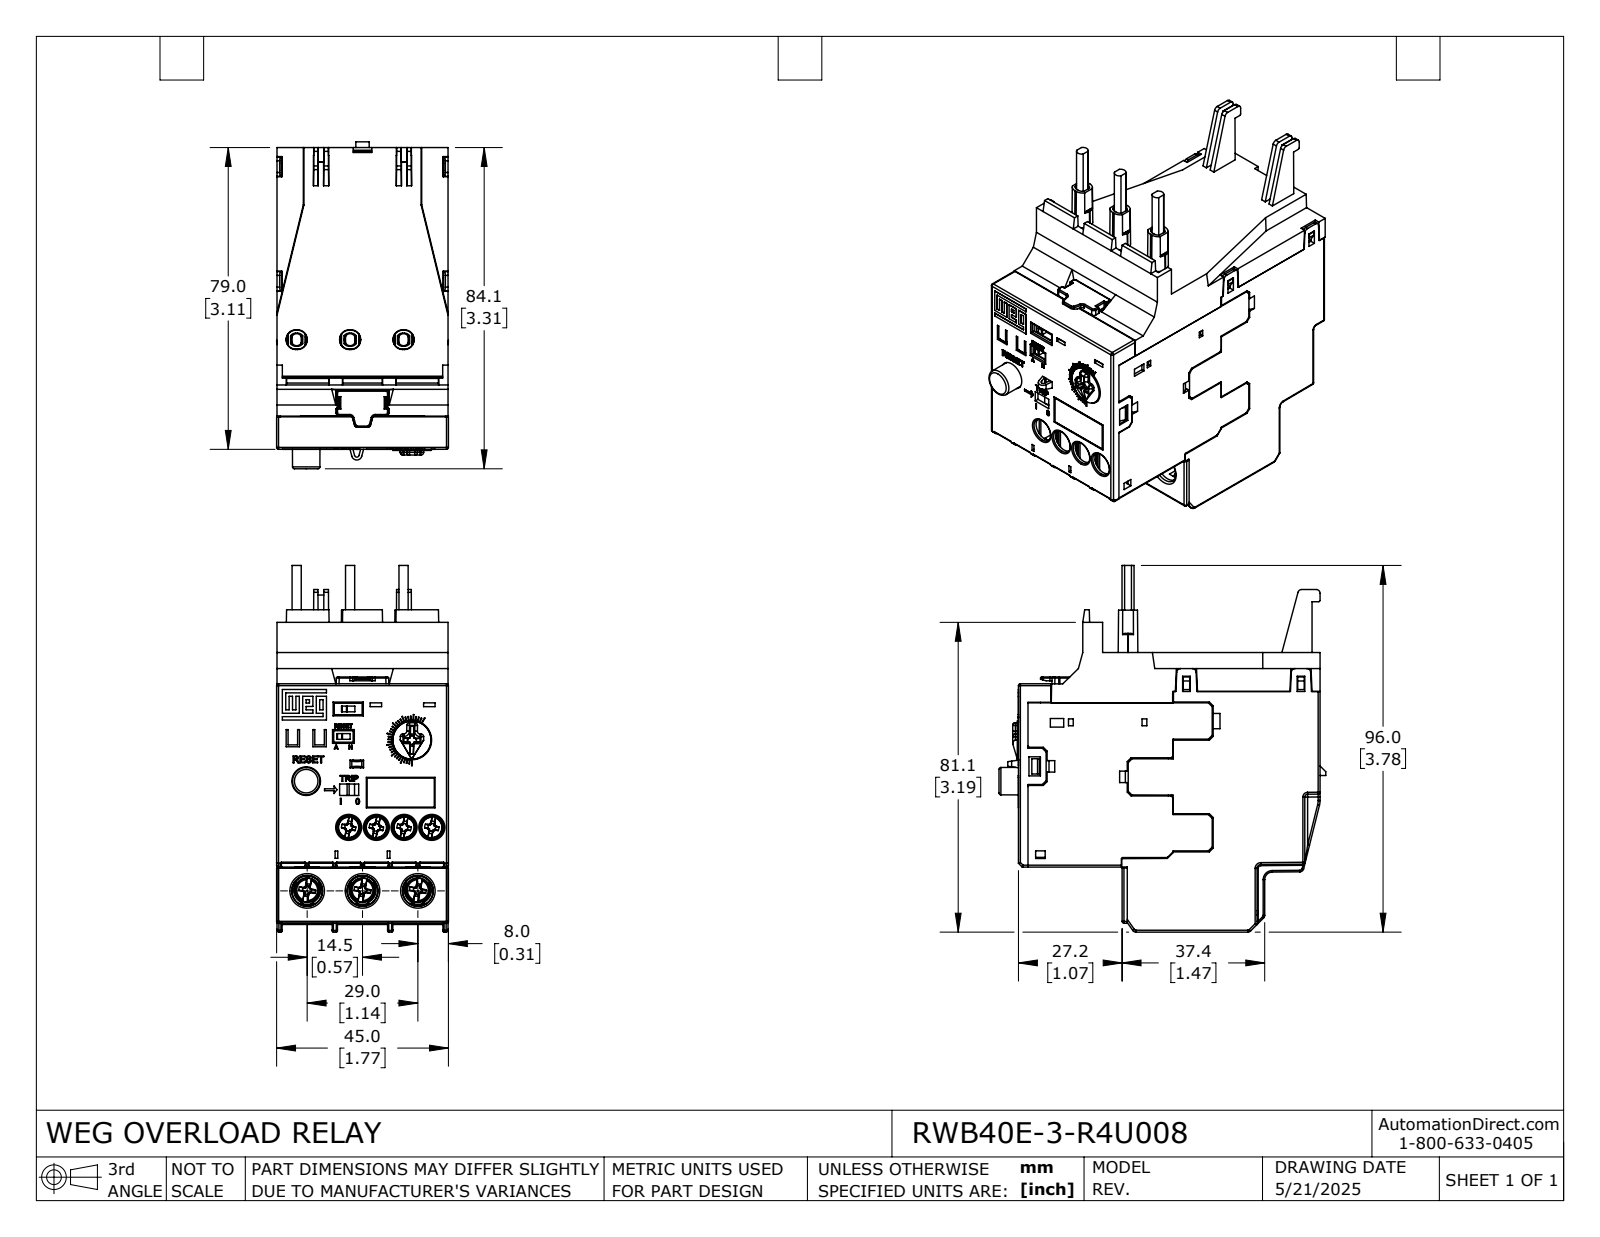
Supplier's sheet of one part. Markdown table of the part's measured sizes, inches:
| quantity | value |
| --- | --- |
| part name | RWB40E-3-R4U008 |
| STEP written by | SolidWorks 2024 (AUTOMOTIVE_DESIGN) |
| units | inches |
| bodies | 38 solids, 3774 faces (2406 planar, 808 cylindrical, 560 other) |
| overall size | 3.78 × 3.37 × 1.772 |
| volume | 10.1 in³ |
| surface area | 114.7 in² |
| round holes (diameter × count) | 0.118 × 9, 0.102 × 6, 0.098 × 4, 0.114 × 3, 0.173 × 3, 0.295 × 1, 0.406 × 1 |
| round bosses / shafts (diameter × count) | 0.138 × 7, 0.087 × 4, 0.295 × 3, 0.165 × 3, 0.114 × 3, 0.098 × 3 |
| partial cylindrical surfaces (radius × count) | 0.012 × 216, 0.02 × 76, 0.039 × 55, 0.008 × 43, 0.01 × 17, 0.037 × 17, 0.016 × 16, 0.059 × 14 |
| main face-to-face distances | 1.764, 0.286, 0.572, 0.049, 0.039, 0.244, 0.857, 0.402, 0.042, 0.53 |
| hole center spacings | 0.286, 0.572, 0.663, 0.857, 0.551, 0.571, 0.662, 0.776 |
